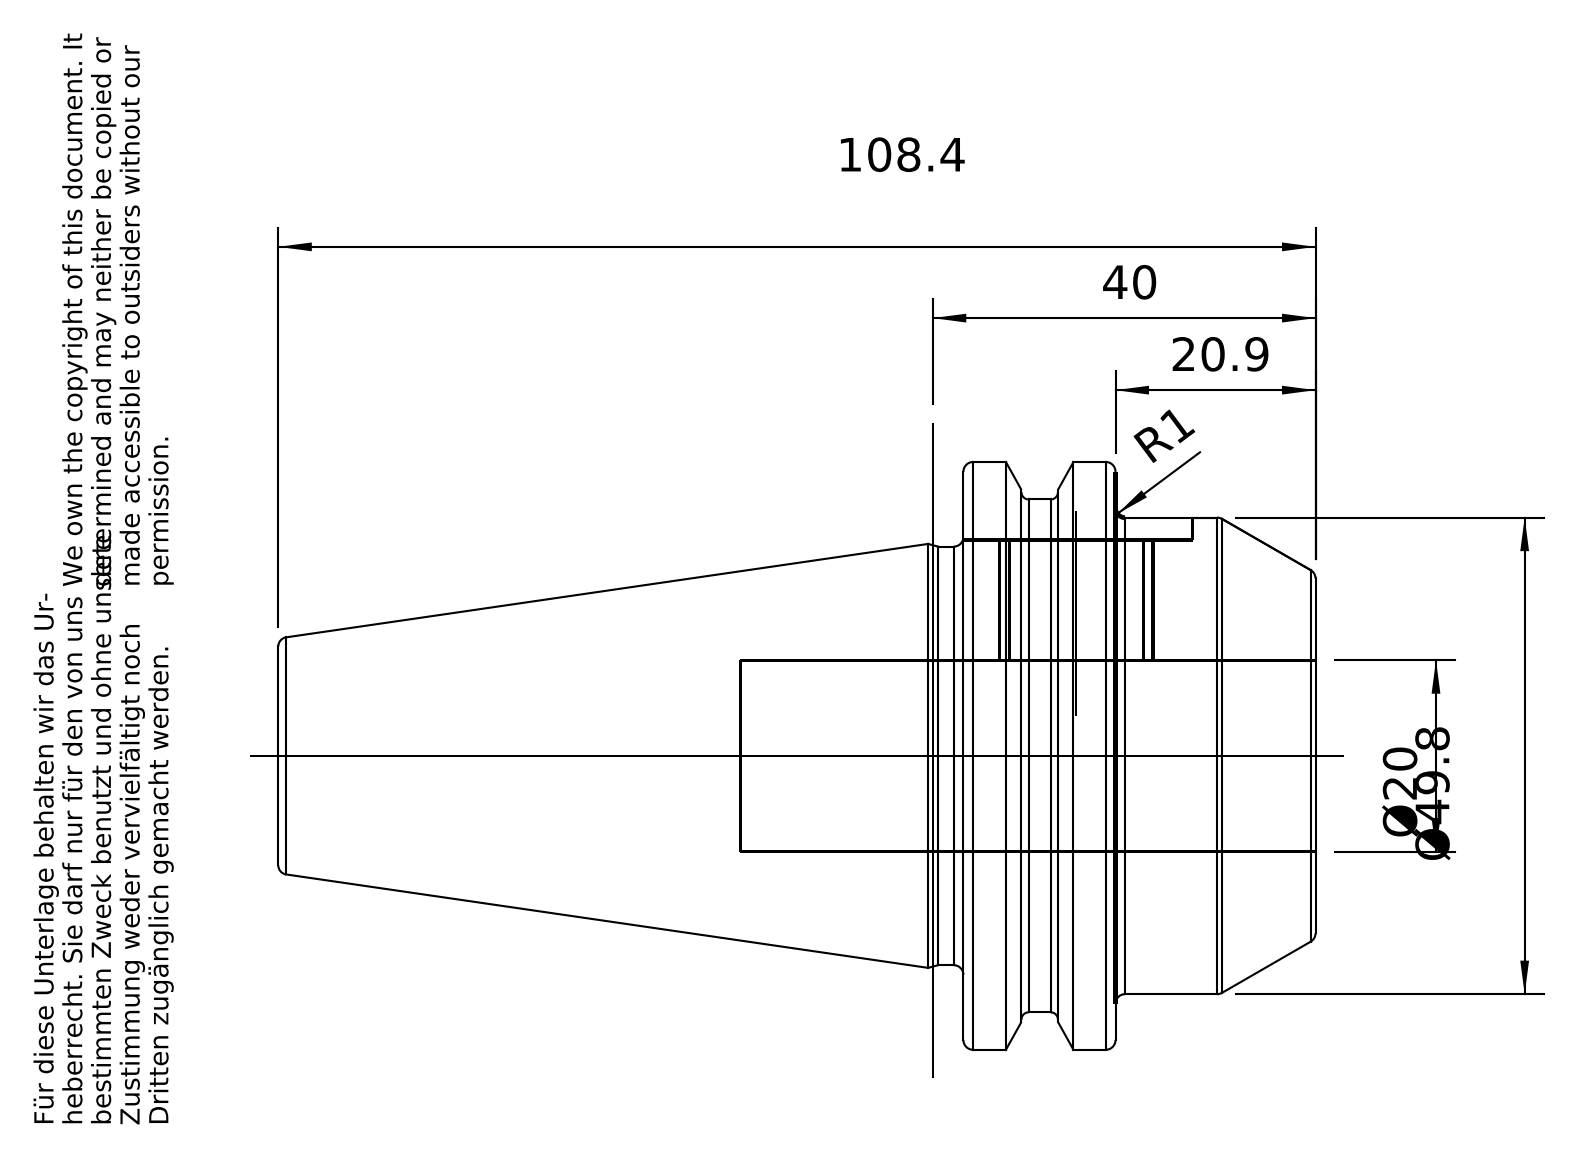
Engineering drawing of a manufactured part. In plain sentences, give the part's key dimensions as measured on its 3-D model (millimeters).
The part is named "40-305-20". Its 3-D file was written by "PRO/ENGINEER BY PARAMETRIC TECHNOLOGY CORPORATION, 2010430 (CONFIG_CONTROL_DESIGN)". It is 1 solid with 101 faces: 25 planar, 28 cylindrical and 48 other. Overall it measures 108.25 by 63.52 by 61.42 millimeters. Its volume is 121 004 cubic millimeters and its surface area 27 154 square millimeters. Round holes: 1 of diameter 13.84, 1 of diameter 14, 1 of diameter 16, 1 of diameter 17.01, 1 of diameter 17.5, 1 of diameter 20. Round bosses or shafts: 1 of diameter 49.8, 1 of diameter 43.75, 1 of diameter 16.01. Partial cylindrical surfaces (rounded edges, fillets, slot ends): 1 of radius 1.35, 1 of radius 28, 1 of radius 31.76. The main face-to-face distances are 36.8, 15.85, 20.95, 16.2, 23.3, 39.15, 60.1, 47.4, 48.15, 71.45.
